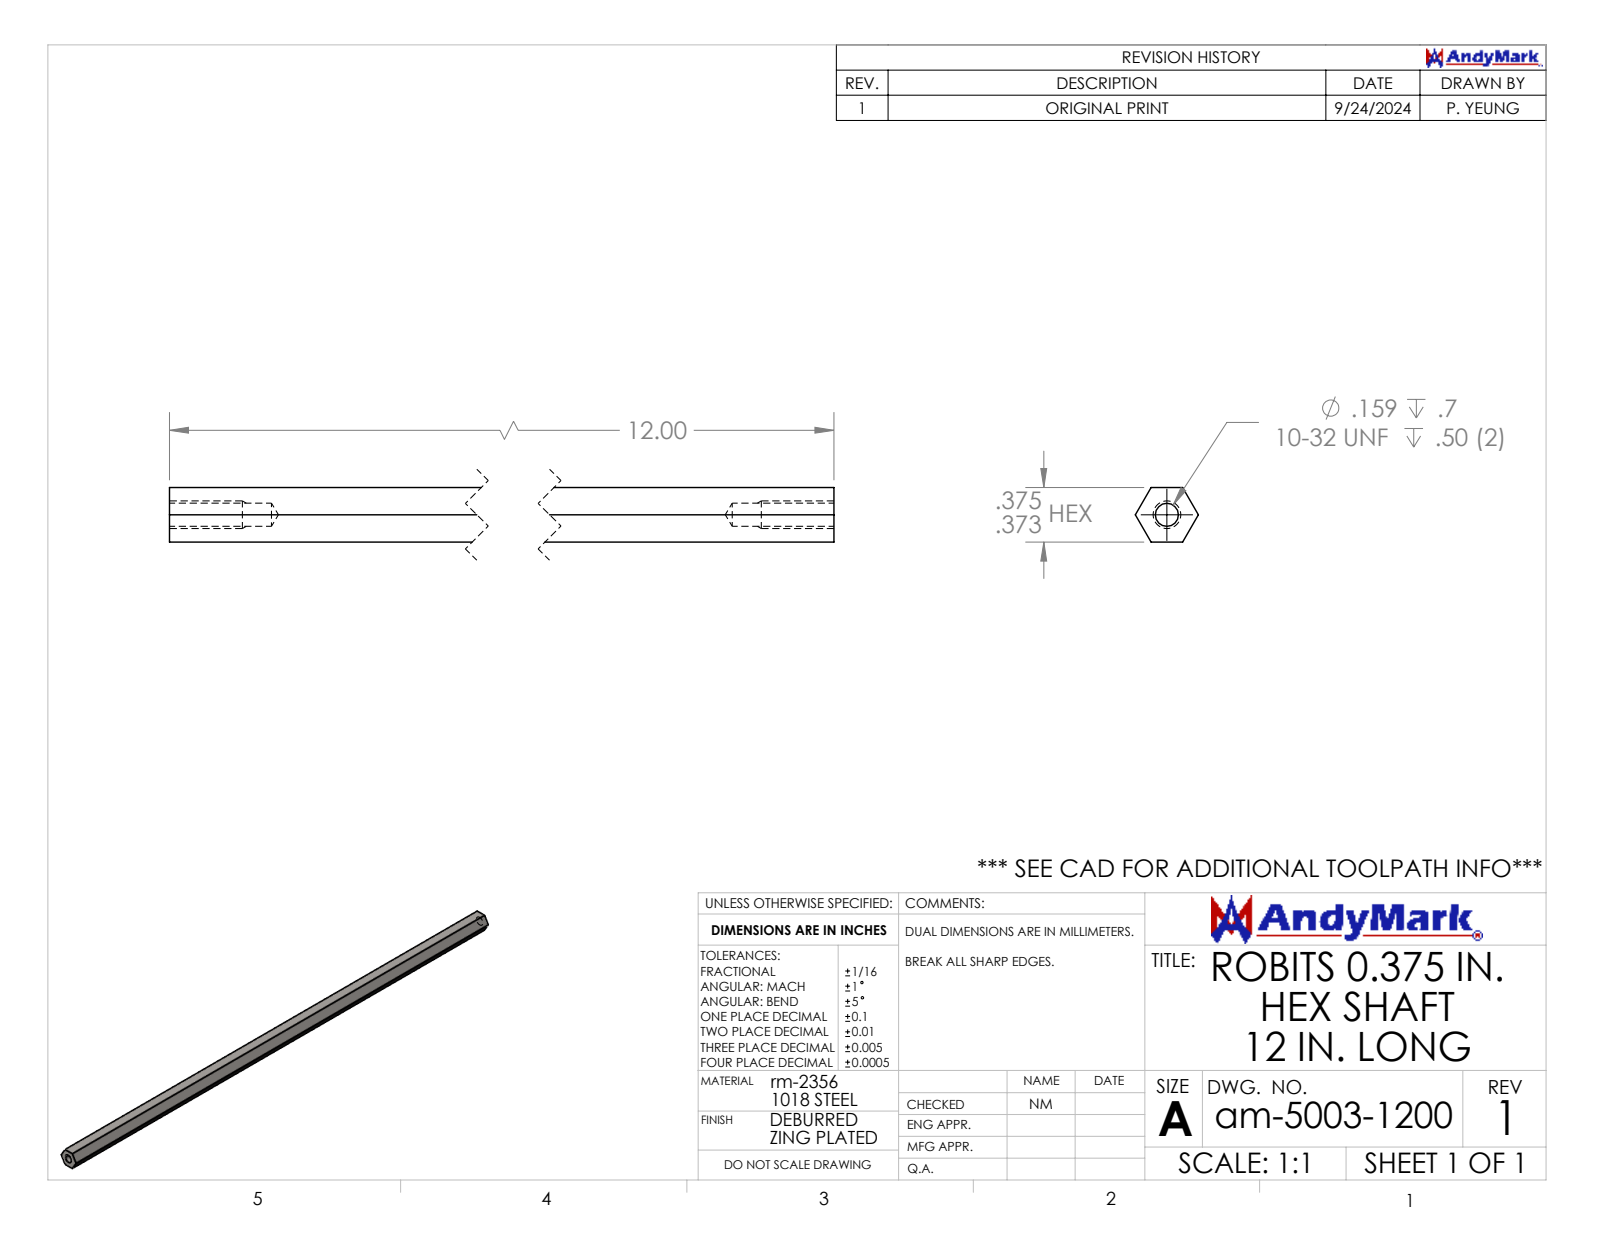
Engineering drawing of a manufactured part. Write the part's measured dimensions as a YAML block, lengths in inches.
part_name: "am-5003-1200 Robits 0.375 in. Hex Shaft 12 in. Long"
step_written_by: "SolidWorks 2024 (AUTOMOTIVE_DESIGN)"
units: inches
bodies: {solids: 1, faces: 16, planar: 8, cylindrical: 4, other: 4}
overall_size: [12, 0.433, 0.375]
volume: 1.433
surface_area: 16.54
round_holes:
  - {diameter: 0.159, count: 1}
face_to_face_distances: [0.375, 12]
